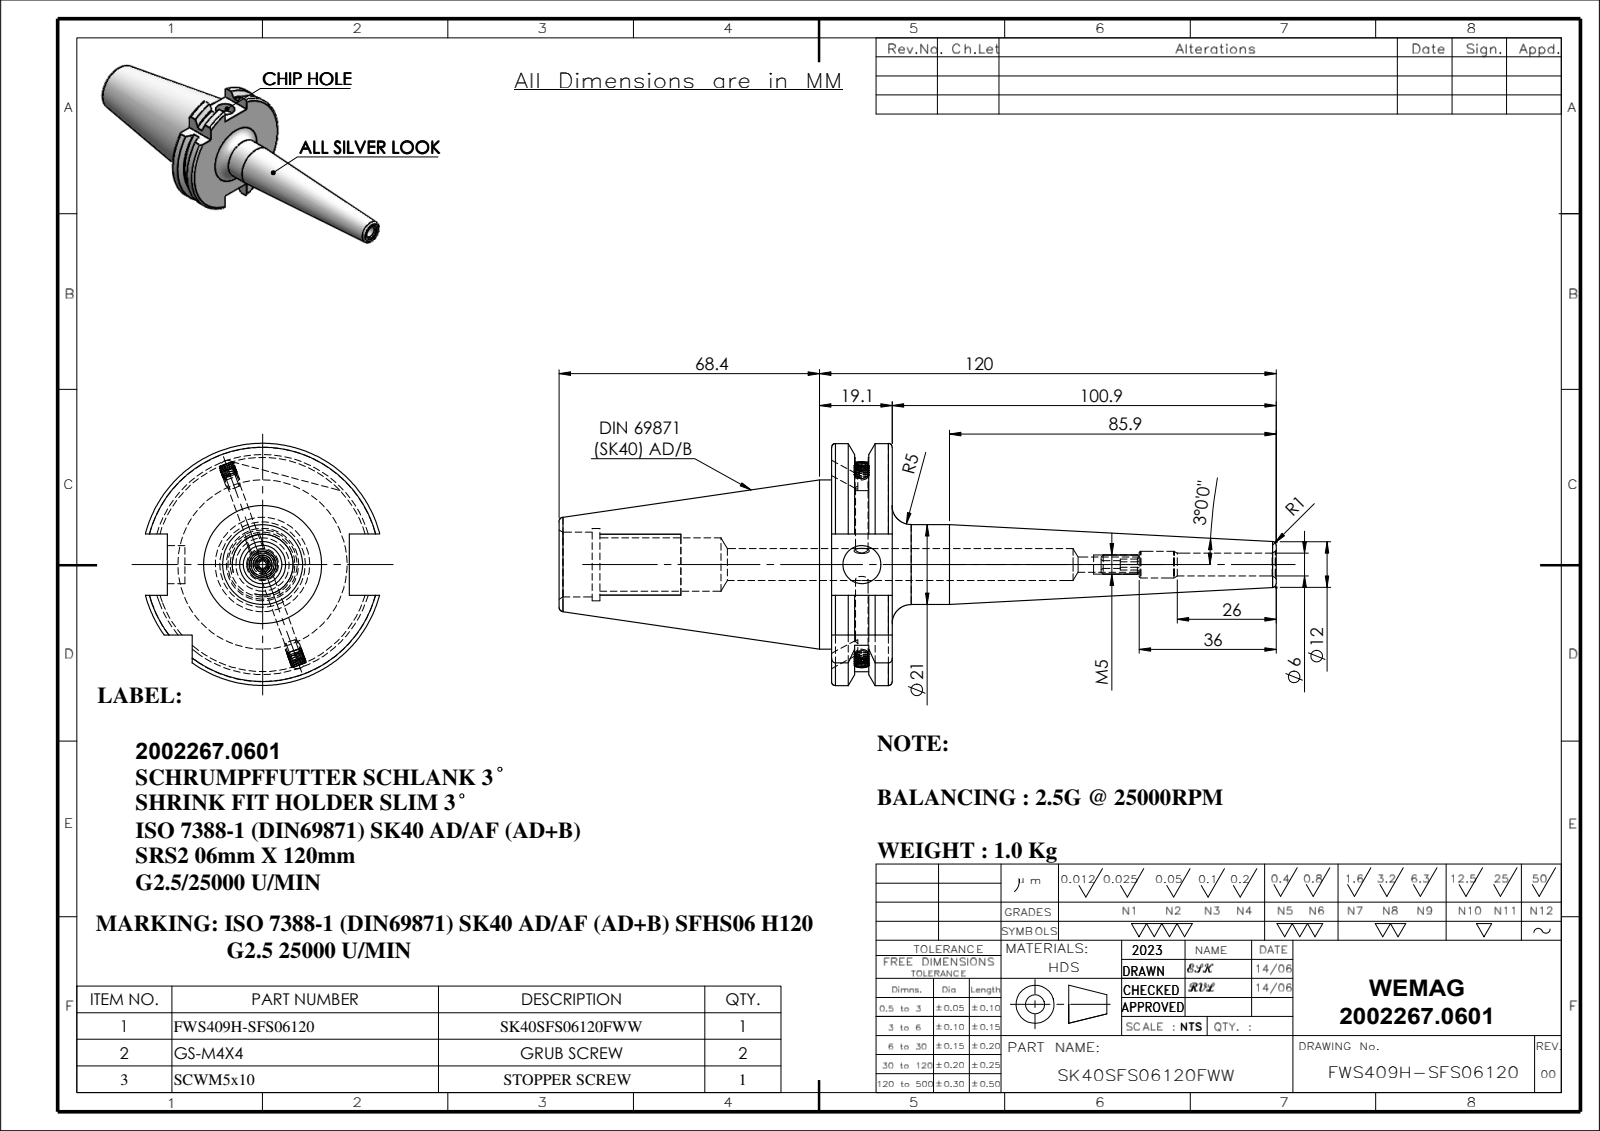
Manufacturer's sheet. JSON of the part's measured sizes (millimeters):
{"part_name": "SK40SFS06120FWW; SCWM5X10; 91406-SRS206120; GS-M4X4_DIN 913 - M4 x 4-N", "step_written_by": "SolidWorks 2018 (CONFIG_CONTROL_DESIGN)", "units": "millimeters", "bodies": {"solids": 4, "faces": 230, "planar": 62, "cylindrical": 60, "other": 108}, "overall_size": [188.4, 63.55, 61.48], "volume_mm3": 123238, "surface_area_mm2": 28473, "round_holes": [[2, 1], [3.3, 1], [4, 1], [6, 1], [7, 1], [8.4, 1], [10, 1], [14, 1], [17, 1], [19, 1]], "round_bosses_or_shafts": [[4, 2], [44.45, 1], [21, 1], [5, 1]], "partial_cylinders_radius": [[28.12, 1], [31.77, 1]], "face_to_face_distances": [15.9, 16.1, 47.8, 71.6, 87.5, 10.7, 60.9, 76.8, 77.62, 66.92]}
